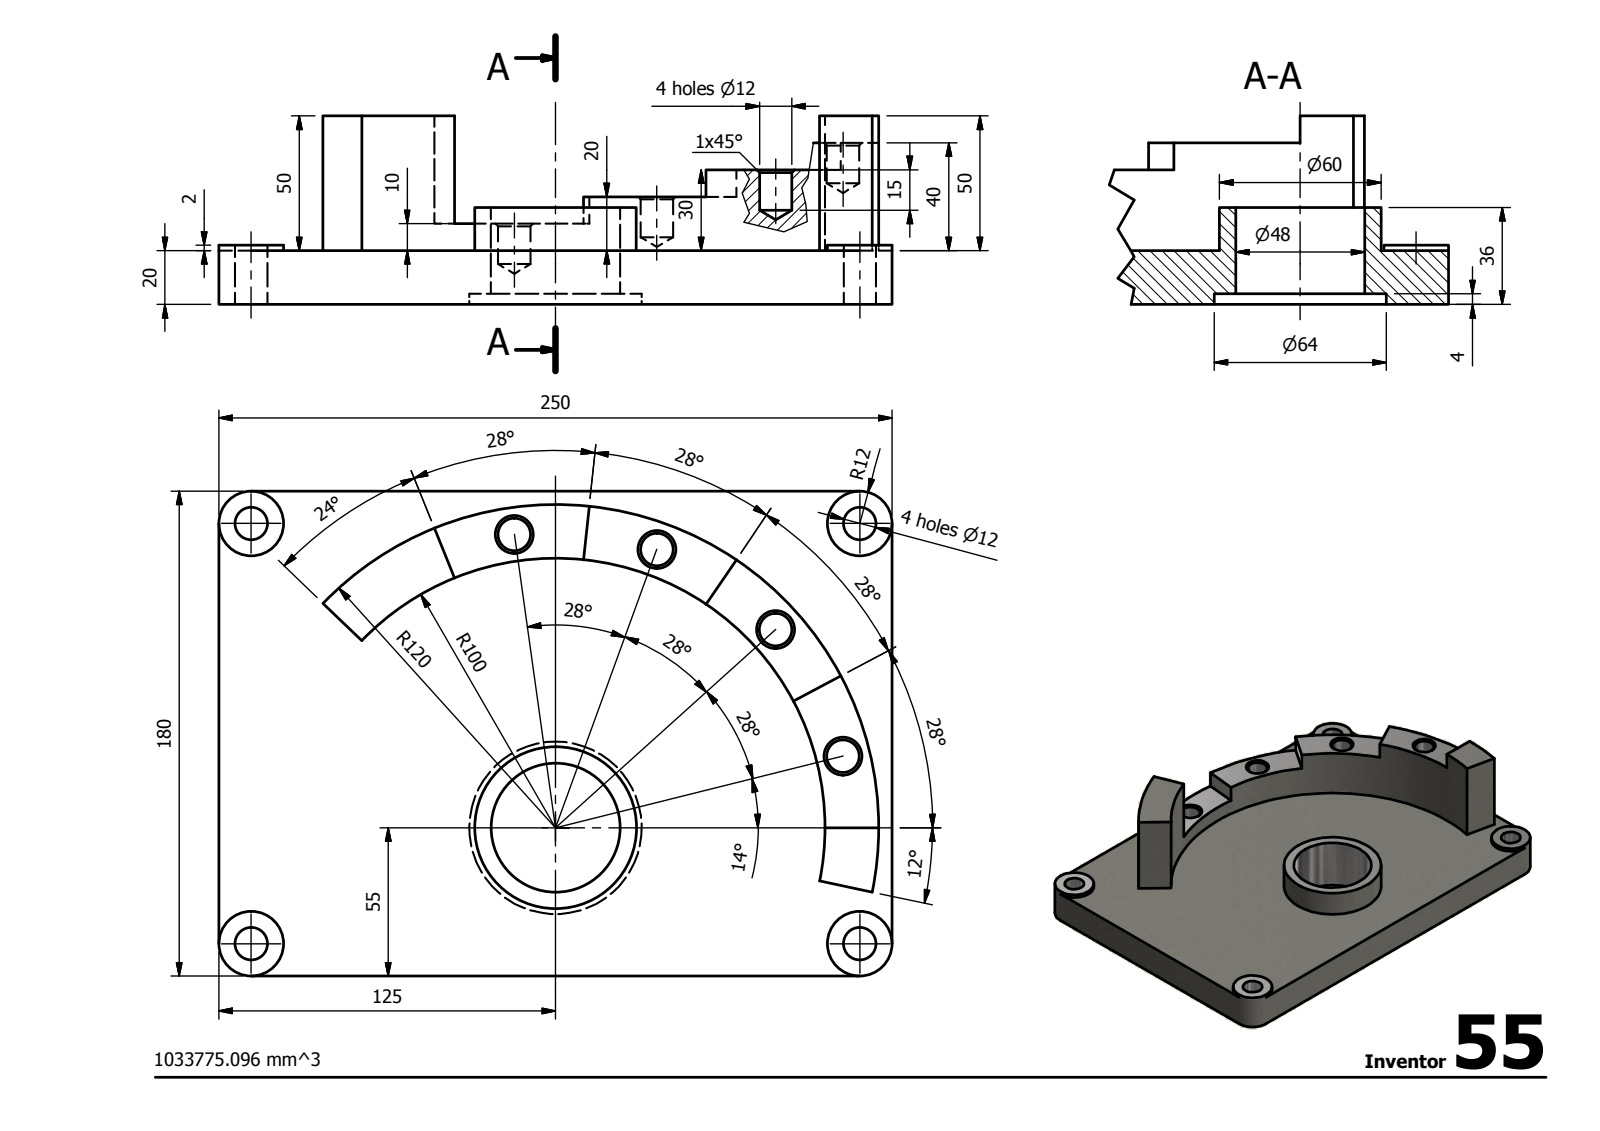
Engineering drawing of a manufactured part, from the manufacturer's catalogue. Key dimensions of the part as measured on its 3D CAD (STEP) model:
STEP written by: Autodesk Inventor 2014 (AUTOMOTIVE_DESIGN)
Units: millimetres
Bodies: 1 solid, 50 faces (25 planar, 17 cylindrical, 8 other)
Overall size (bounding box): 250 × 180 × 70
Volume: 1 034 000 mm³ · Surface area: 137 990 mm²
Round holes (diameter × count): ⌀12 ×8, ⌀48 ×1, ⌀64 ×1
Round bosses / shafts (diameter × count): ⌀24 ×4, ⌀60 ×1
Partial cylindrical surfaces — rounded edges, fillets, slot ends (radius × count): R100 ×1, R120 ×1
Main face-to-face distances: 20, 10, 180, 30, 250, 40, 16, 4, 50, 18
Hole centre spacings: 110, 53.22, 103.29, 120.9, 156, 159.81, 226, 274.61
